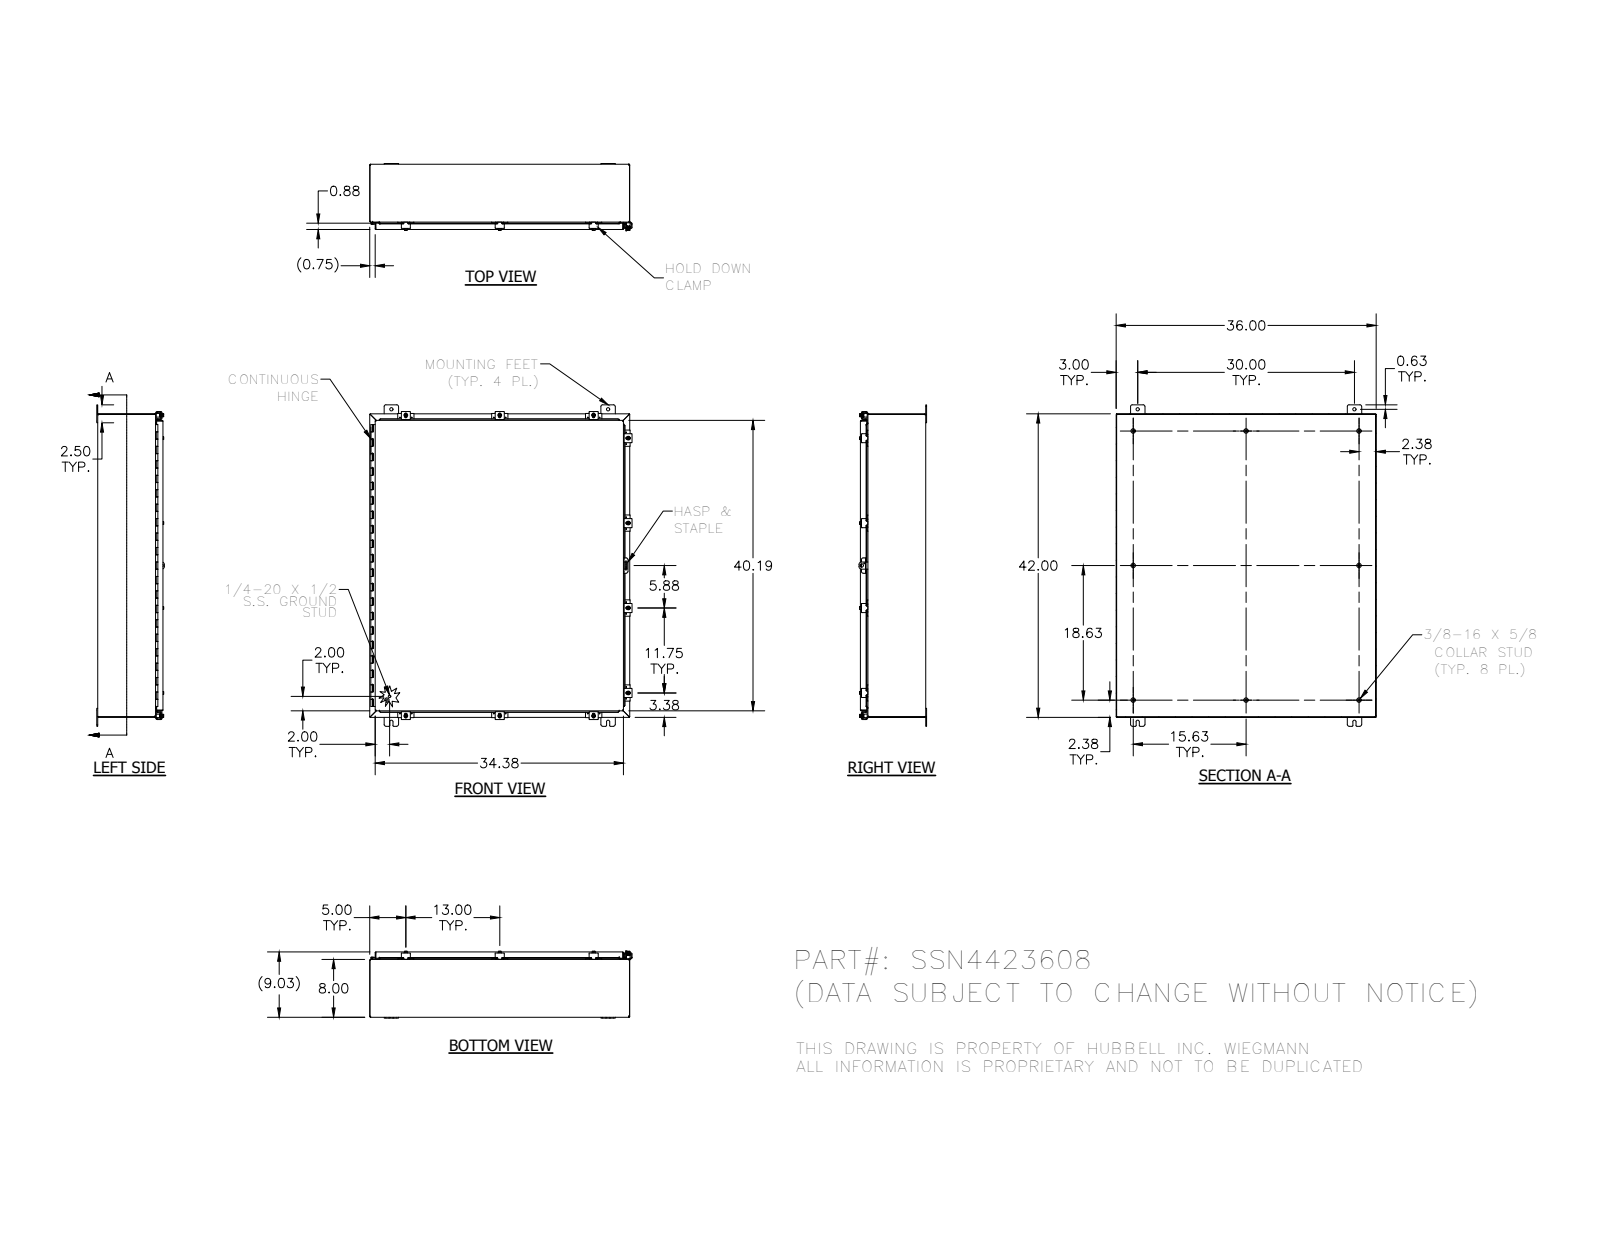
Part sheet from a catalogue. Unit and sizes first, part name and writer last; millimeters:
Units: millimetres
Overall size (bounding box): 1130.3 × 922.3 × 237.6
Round holes (diameter × count): ⌀2.8 ×20, ⌀5.4 ×10, ⌀7.1 ×10, ⌀7.6 ×10, ⌀11.1 ×4, ⌀3.2 ×1, ⌀4 ×1, ⌀12.7 ×1
Round bosses / shafts (diameter × count): ⌀6.4 ×12, ⌀13.2 ×10, ⌀12.7 ×10, ⌀8.9 ×10, ⌀15.9 ×8, ⌀8.4 ×8, ⌀8.6 ×1, ⌀3 ×1
Partial cylindrical surfaces — rounded edges, fillets, slot ends (radius × count): R0.8 ×117, R3.2 ×41, R6.4 ×37, R0.8 ×23, R2.7 ×23, R3.6 ×20, R1.6 ×19, R2.5 ×14
Main face-to-face distances: 1.9, 227.6, 225.7, 229.4, 912.5, 1064.9, 201.3, 26.2, 910.6, 914.4
Hole centre spacings: 22.3, 330.2, 1048.9, 309.7, 351, 1091.5, 1093.5, 1105.9
Volume: 6 078 000 mm³ · Surface area: 6 321 000 mm²
Bodies: 71 solids, 2841 faces (1070 planar, 1270 cylindrical, 501 other)
Part name (STEP PRODUCT): SSN44236LID; SSN4423608; 328141L; 38859 (+8 more)
STEP written by: SolidWorks 2014 (AUTOMOTIVE_DESIGN)
